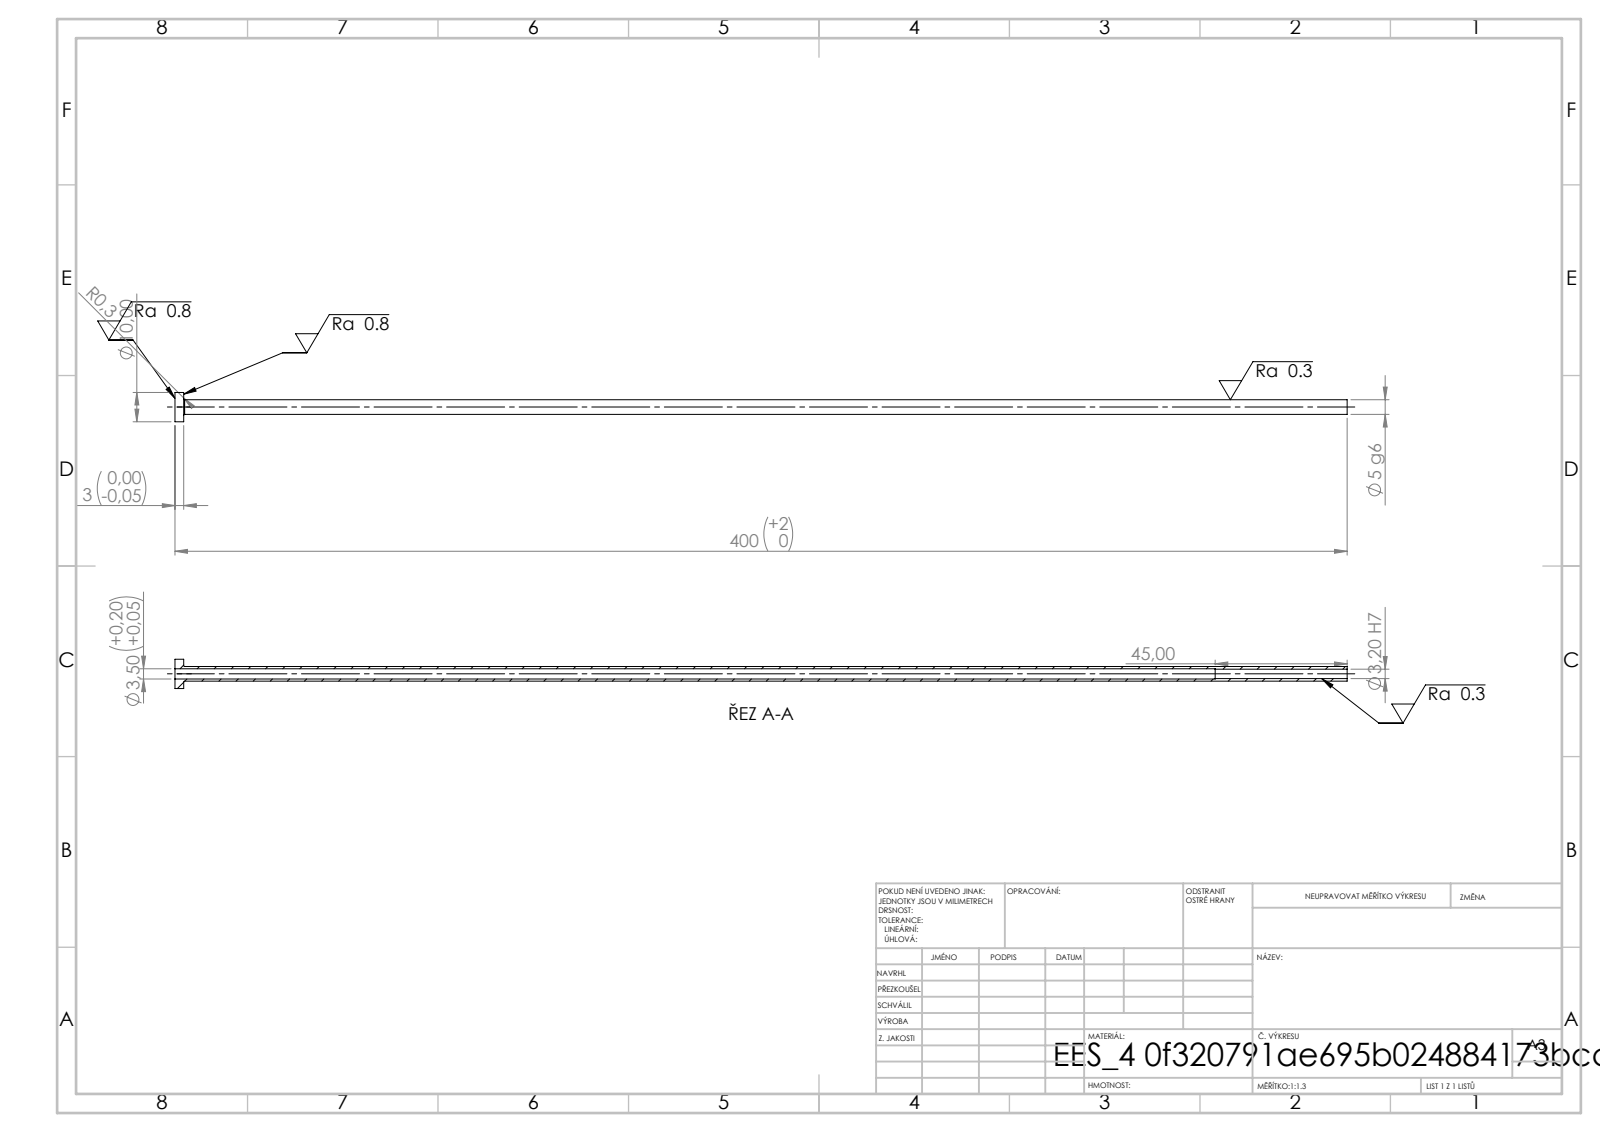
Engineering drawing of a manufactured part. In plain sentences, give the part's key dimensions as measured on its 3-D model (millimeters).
Its 3-D file was written by "SolidWorks 2019 (CONFIG_CONTROL_DESIGN)". It is 1 solid with 14 faces: 4 planar, 8 cylindrical and 2 other. Overall it measures 400 by 10 by 10 millimeters. Its volume is 4 254 cubic millimeters and its surface area 10 825 square millimeters. Round holes: 1 of diameter 3.2, 1 of diameter 3.5. Round bosses or shafts: 1 of diameter 10, 1 of diameter 5. The main face-to-face distances are 3, 400, 397, 355, 352, 45.
